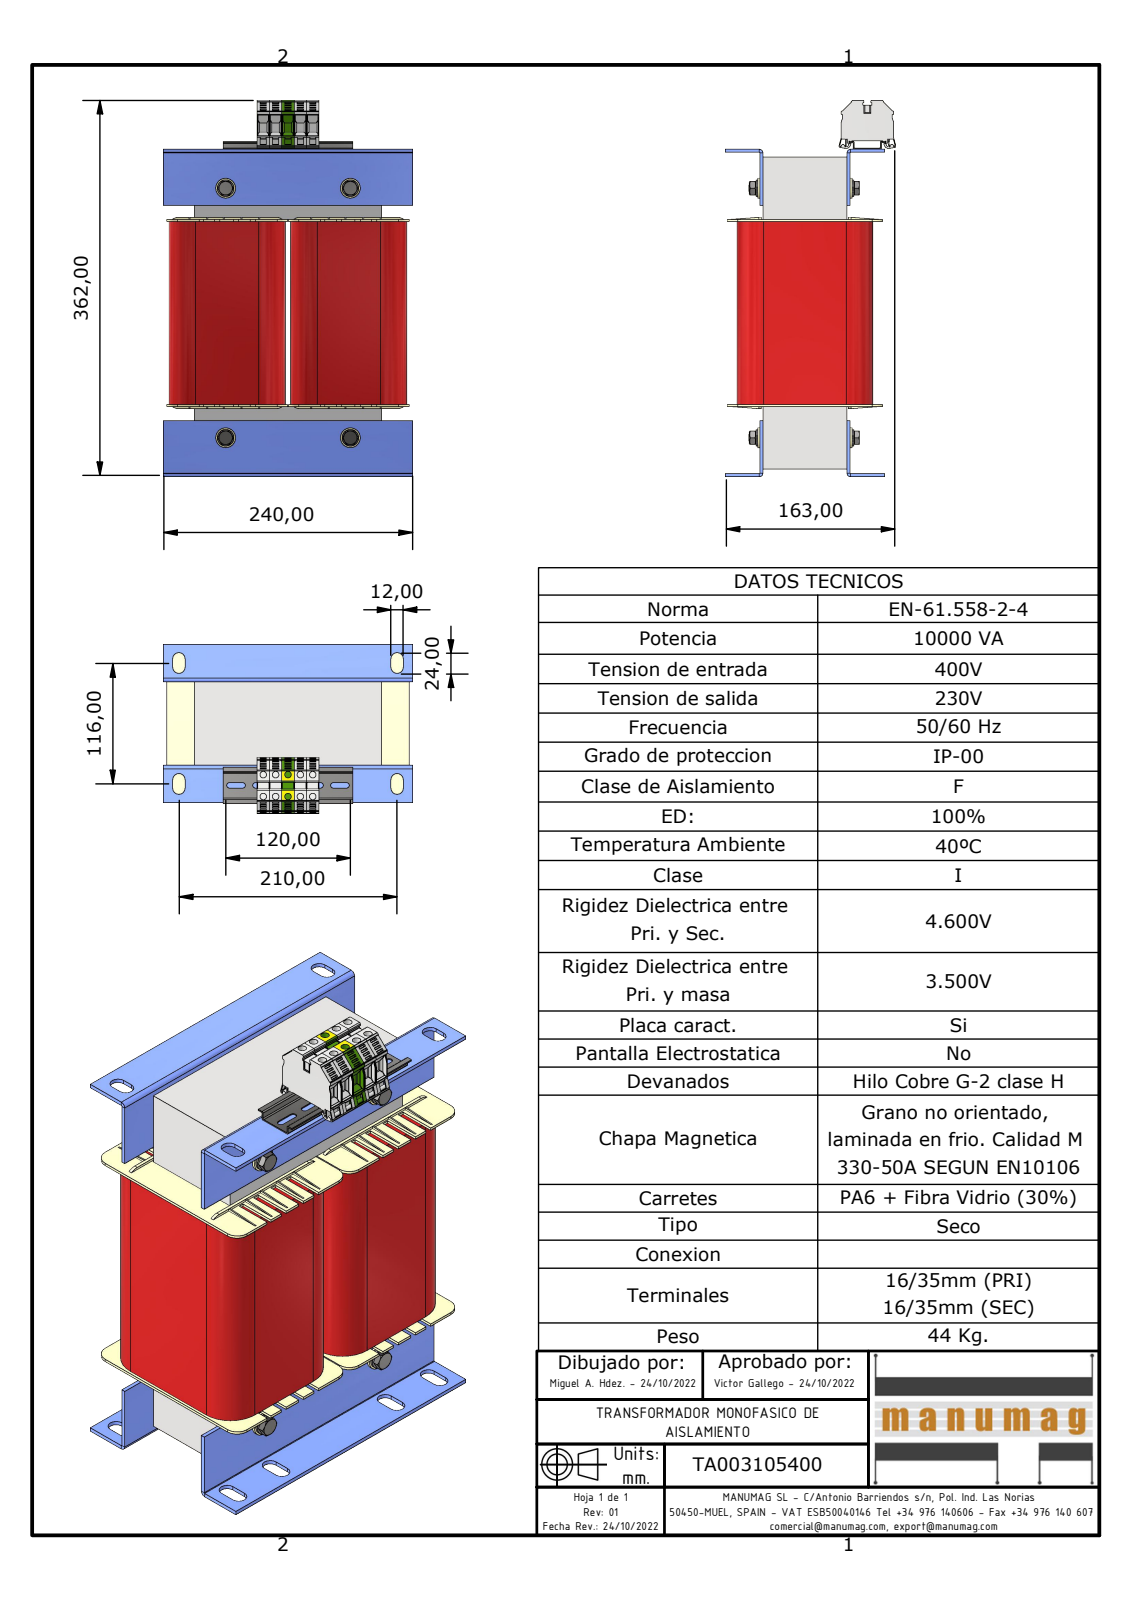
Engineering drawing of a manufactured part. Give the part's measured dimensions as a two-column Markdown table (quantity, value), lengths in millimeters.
| quantity | value |
| --- | --- |
| part name | TA003105400; UI300 x 180 - 80 (Rc60); RC 60 UI INFERIOR; RC 60 UI SUPERIOR (+8 more) |
| STEP written by | Autodesk Inventor 2023 (AUTOMOTIVE_DESIGN) |
| units | millimeters |
| bodies | 37 solids, 3242 faces (1958 planar, 1030 cylindrical, 254 other) |
| overall size | 362.1 × 240 × 162.6 |
| volume | 6 852 000 mm³ |
| surface area | 1 008 000 mm² |
| round holes (diameter × count) | 6.3 × 10, 6.65 × 4, 8 × 4, 8.4 × 4, 13 × 4 |
| round bosses / shafts (diameter × count) | 19 × 4, 16 × 4, 11.4 × 4, 9.6 × 4, 7.32 × 4 |
| partial cylindrical surfaces (radius × count) | 0.3 × 258, 1 × 24, 6 × 24, 0.25 × 16, 10 × 16, 2 × 10, 2.6 × 10, 0.5 × 8 |
| main face-to-face distances | 1, 117, 22.37, 23.37, 1.5, 3, 83, 60, 22.06, 0.31 |
| hole center spacings | 11.9, 24.14, 23.8, 31.74, 21, 35.7, 41.42, 47.6 |
